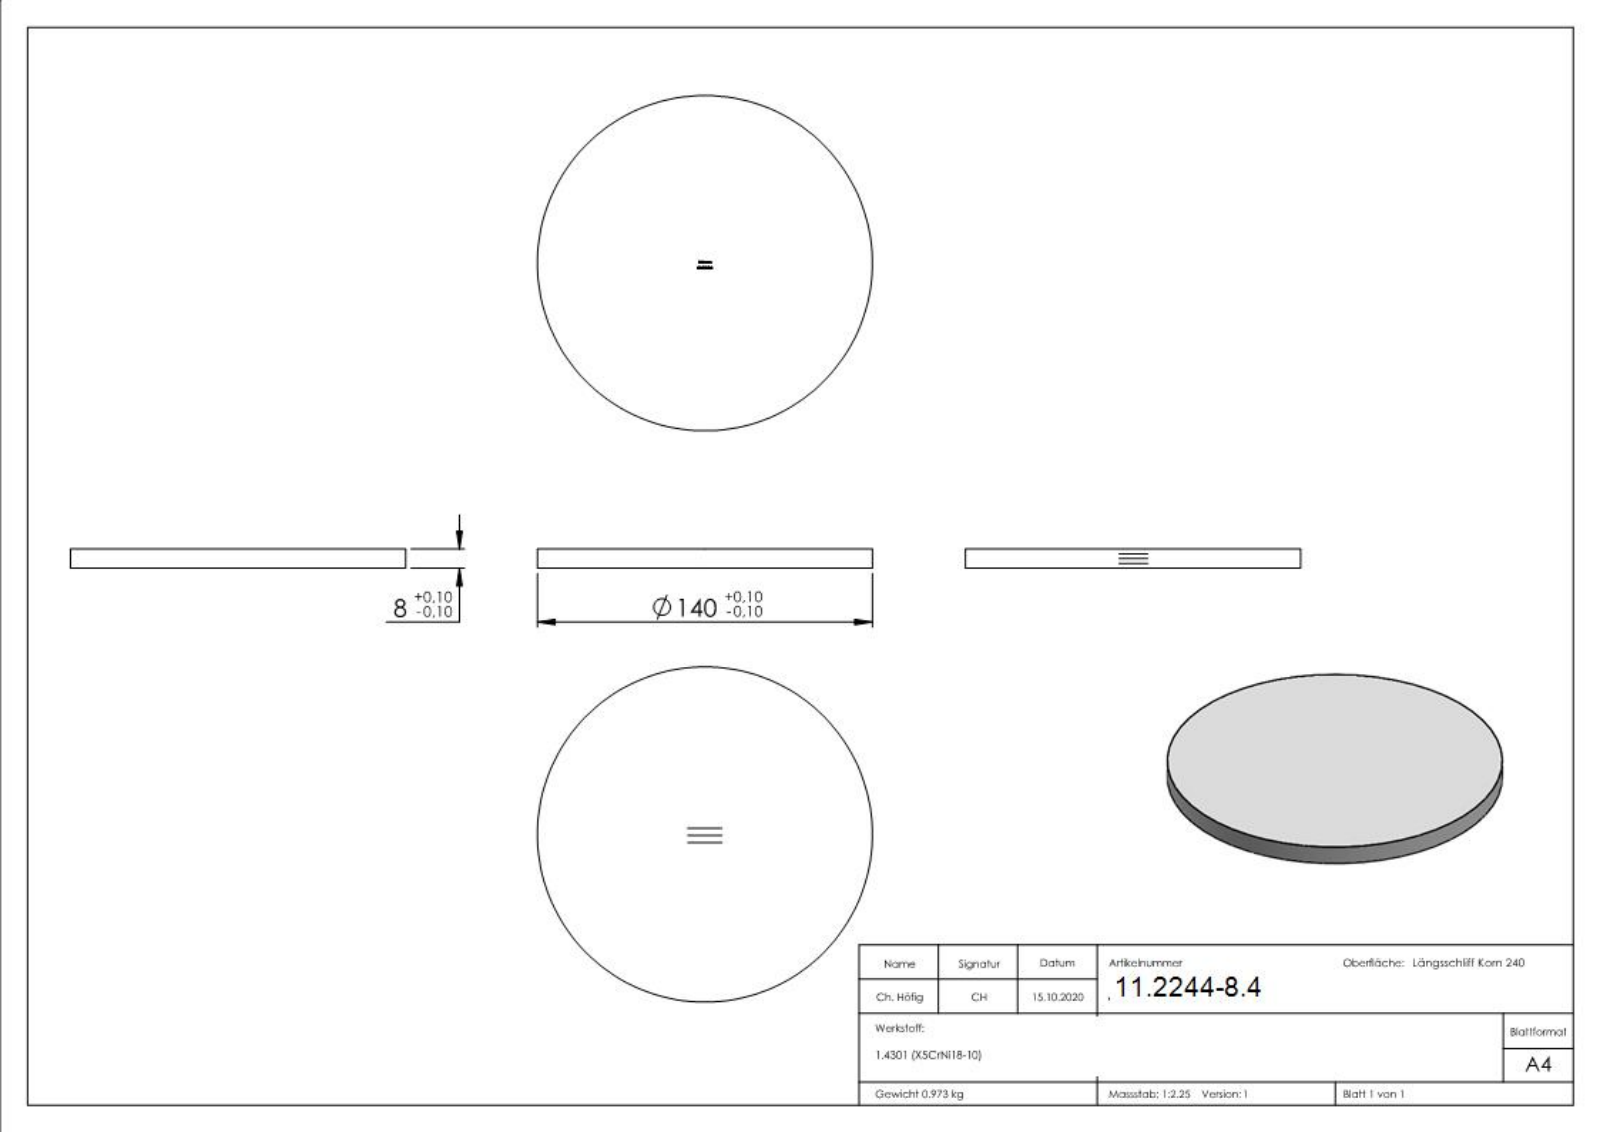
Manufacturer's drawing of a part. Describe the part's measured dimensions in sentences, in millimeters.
The part is named "53140-240-8". Its 3-D file was written by "SolidWorks 2018 (CONFIG_CONTROL_DESIGN)". It is 1 solid with 252 faces: 139 planar, 2 cylindrical and 111 other. Overall it measures 140 by 140 by 8 millimeters. Its volume is 123 150 cubic millimeters and its surface area 34 312 square millimeters. Round bosses or shafts: 1 of diameter 140. The main face-to-face distances are 8, 7.9, 0.83, 2.61, 3.03, 1.78, 0.95, 0.76, 2.77, 1.02.
